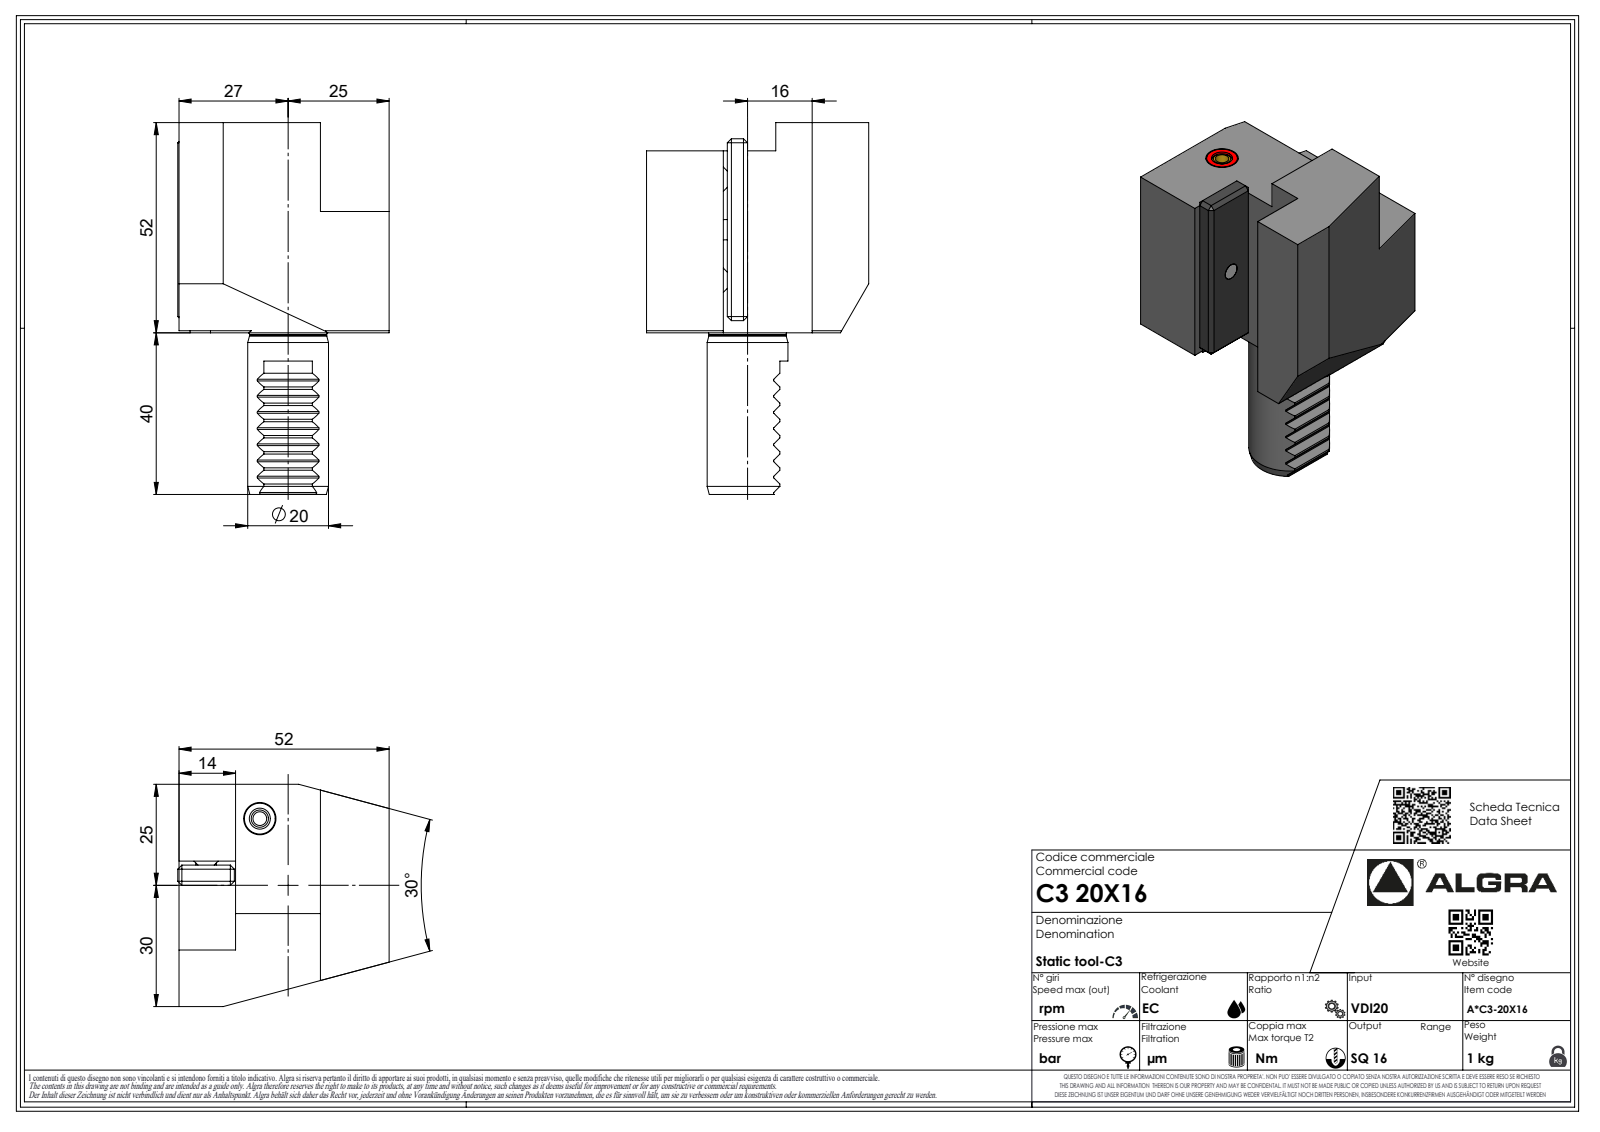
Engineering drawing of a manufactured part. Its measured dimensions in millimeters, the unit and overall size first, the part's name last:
Units: millimetres
Overall size (bounding box): 92 × 55 × 52.3
Round holes (diameter × count): ⌀2.1 ×1
Round bosses / shafts (diameter × count): ⌀20 ×1, ⌀19.1 ×1, ⌀6.37 ×1, ⌀1.7 ×1
Partial cylindrical surfaces — rounded edges, fillets, slot ends (radius × count): R0.3 ×8, R0.33 ×7, R0.52 ×7, R3.7 ×7, R0.21 ×1, R25 ×1
Main face-to-face distances: 52, 14, 30, 38, 45, 21, 35, 22, 17, 7
Volume: 109 110 mm³ · Surface area: 18 447 mm²
Bodies: 1 solid, 302 faces (206 planar, 39 cylindrical, 57 other)
Part name (STEP PRODUCT): C320X16
STEP written by: SolidWorks 2023 (AUTOMOTIVE_DESIGN)
